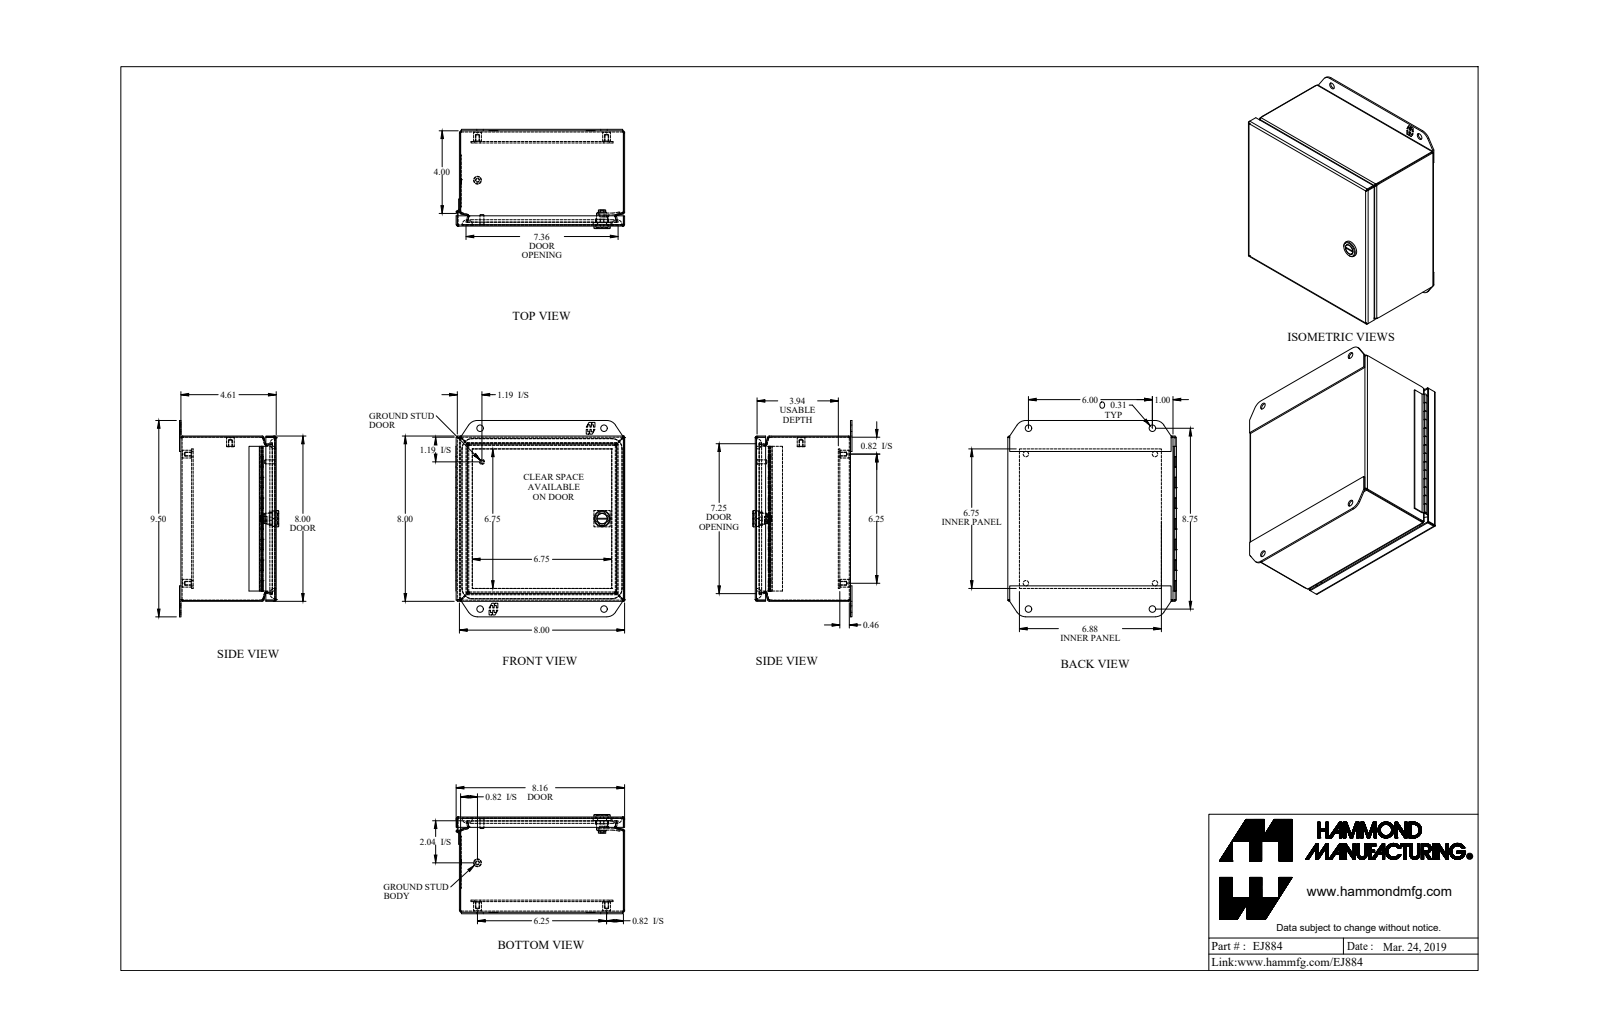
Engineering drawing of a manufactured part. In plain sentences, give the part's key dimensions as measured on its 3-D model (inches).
The part is named "EJ884_Default". Its 3-D file was written by "SolidWorks 2019 (CONFIG_CONTROL_DESIGN)". It is 16 solids with 643 faces: 361 planar, 190 cylindrical and 92 other. Overall it measures 9.5 by 8.165 by 4.805 inches. Its volume is 24.92 cubic inches and its surface area 818.2 square inches. Round holes: 5 of diameter 0.156, 4 of diameter 0.265, 4 of diameter 0.313, 1 of diameter 0.05, 1 of diameter 0.516. Round bosses or shafts: 5 of diameter 0.375, 1 of diameter 0.788, 1 of diameter 0.535, 1 of diameter 0.496, 1 of diameter 0.435, 1 of diameter 0.25, 1 of diameter 0.188, 1 of diameter 0.1. Partial cylindrical surfaces (rounded edges, fillets, slot ends): 16 of radius 0.029, 16 of radius 0.086, 10 of radius 0.281, 4 of radius 0.25, 4 of radius 0.499, 4 of radius 0.5, 2 of radius 0.06, 2 of radius 0.539. The main face-to-face distances are 0.057, 4.554, 7.943, 0.072, 0.589, 8, 7.886, 4.611, 4.497, 0.46. The hole center spacings are 1.256, 1.256, 3.133, 6, 6.25, 6.25, 6.251, 6.793.
